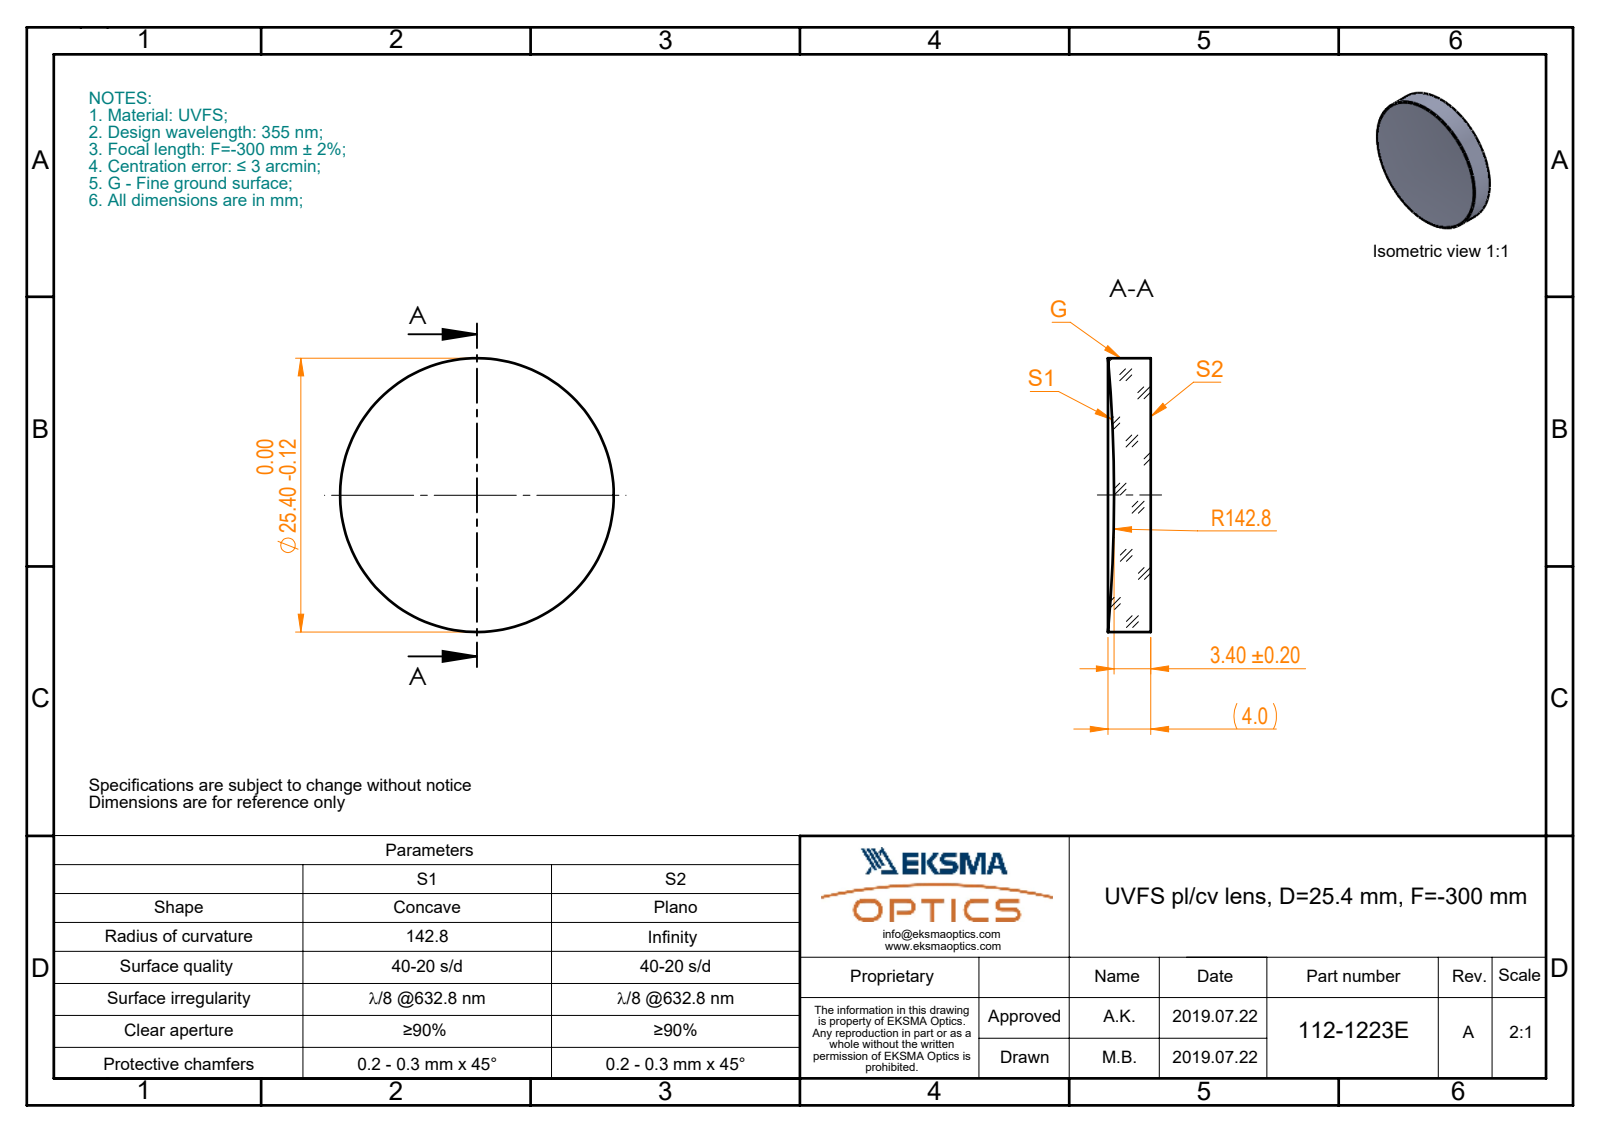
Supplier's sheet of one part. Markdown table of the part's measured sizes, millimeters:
| quantity | value |
| --- | --- |
| part name | 112-1223E UVFS pl-cv 25.4 F-300 |
| STEP written by | SolidWorks 2017 (CONFIG_CONTROL_DESIGN) |
| units | millimeters |
| bodies | 1 solid, 5 faces (1 planar, 2 cylindrical, 2 other) |
| overall size | 25.4 × 25.4 × 3.97 |
| volume | 1 866 mm³ |
| surface area | 1 331 mm² |
| round bosses / shafts (diameter × count) | 25.4 × 1 |
